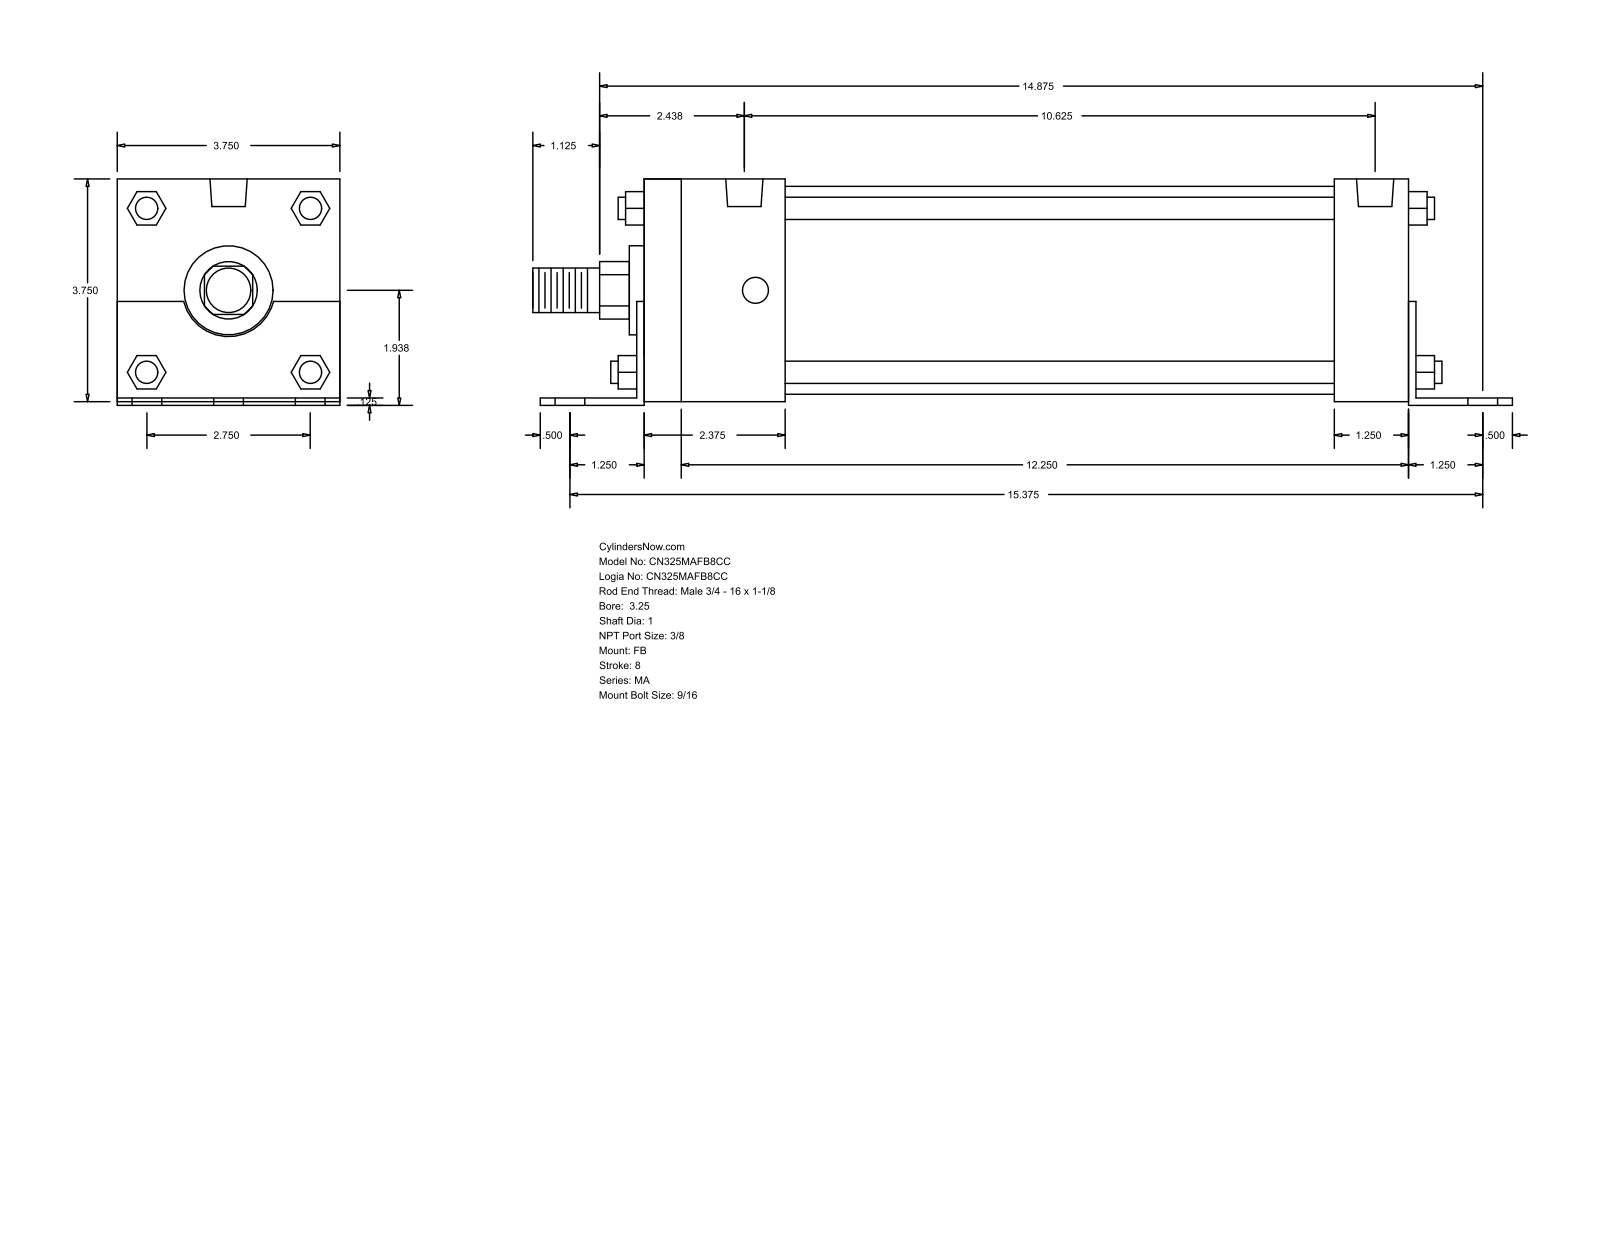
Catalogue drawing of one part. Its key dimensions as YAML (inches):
part_name: "MA_FB__0325_1"
step_written_by: "GSSL Pune (CONFIG_CONTROL_DESIGN)"
units: inches
bodies: {solids: 0, faces: 140, planar: 105, cylindrical: 35, other: 0}
overall_size: [16.5, 3.813, 3.75]
round_holes:
  - {diameter: 0.563, count: 6}
  - {diameter: 0.437, count: 4}
  - {diameter: 0.627, count: 2}
round_bosses_or_shafts:
  - {diameter: 0.375, count: 4}
  - {diameter: 3.5, count: 1}
  - {diameter: 1.5, count: 1}
  - {diameter: 1, count: 1}
  - {diameter: 0.75, count: 1}
partial_cylinders:
  - {radius: 0.484, count: 1}
  - {radius: 0.78, count: 1}
face_to_face_distances: [3.75, 0.125, 0.063, 3.812, 0.062, 3.687, 0.125, 12.875, 13.125, 13]
hole_center_spacings: [1.375, 15.436, 15.375, 2.275, 2.427, 2.75, 3.243, 3.414]
